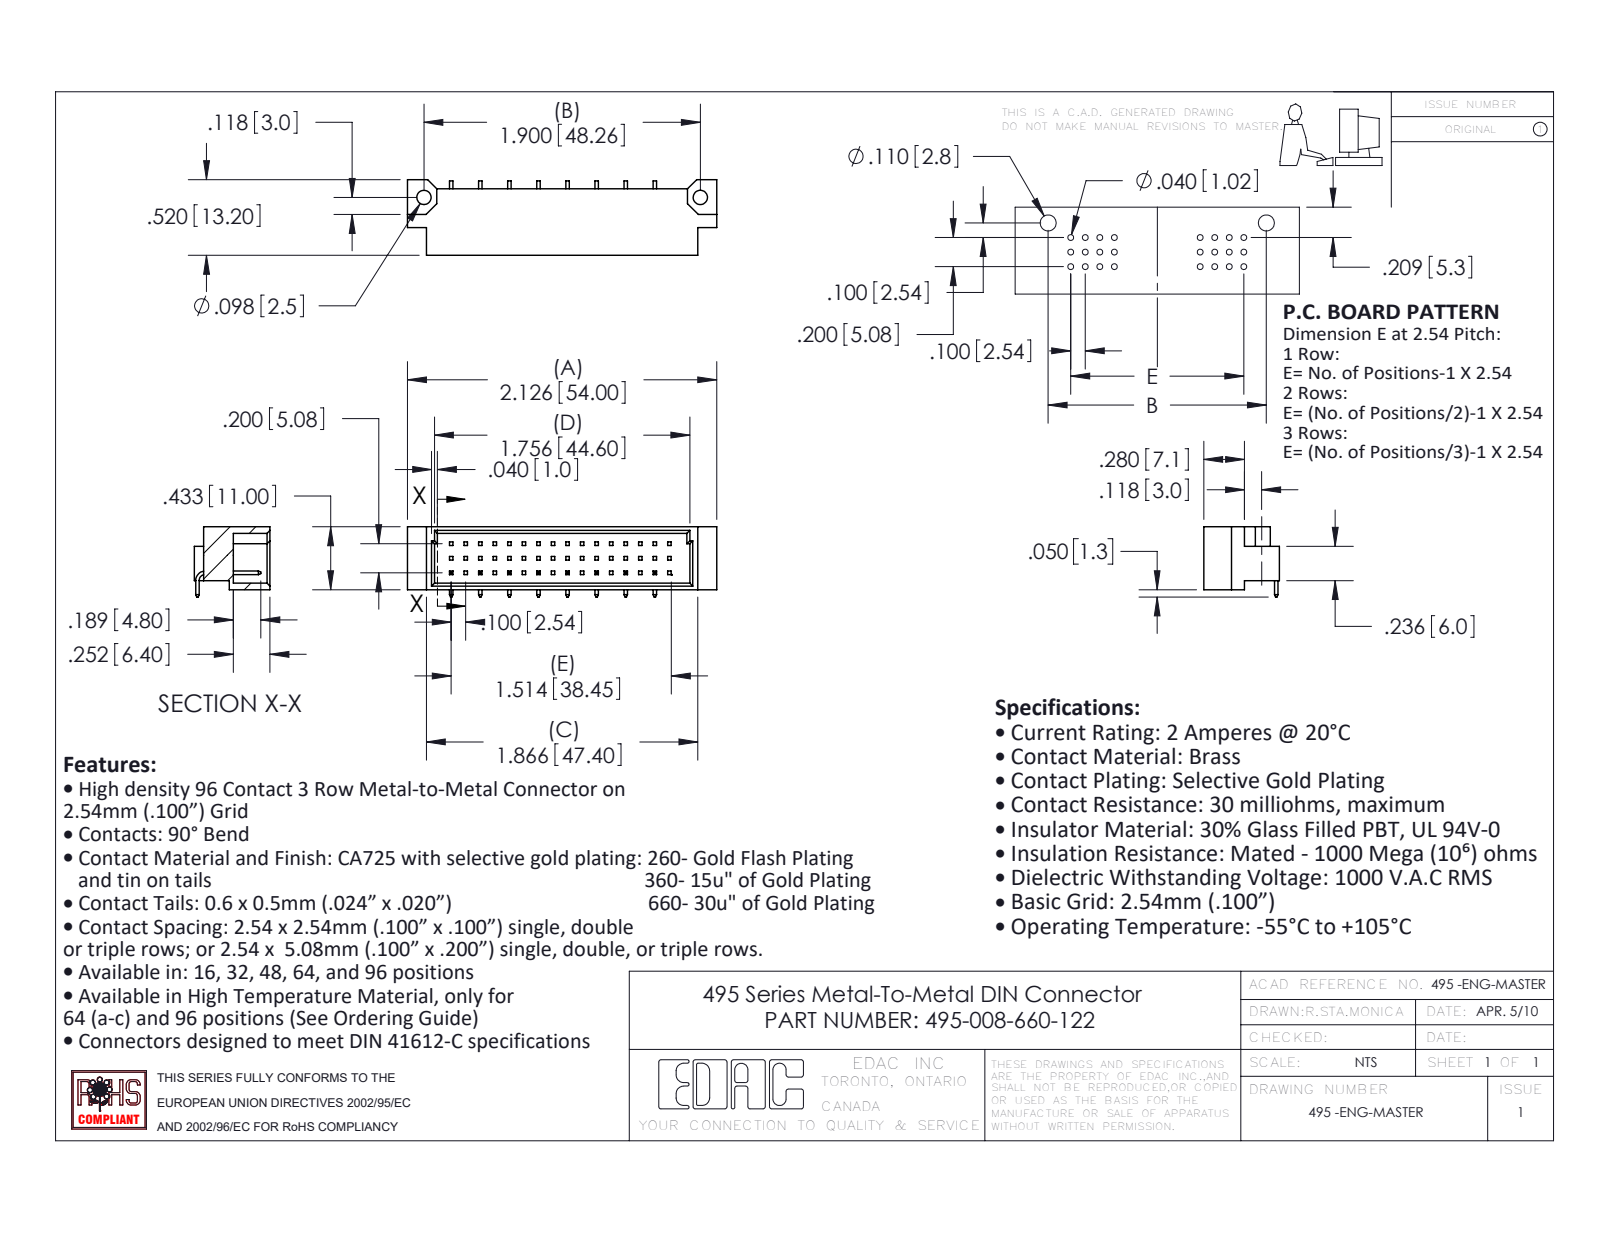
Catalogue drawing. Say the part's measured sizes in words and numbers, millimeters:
The part is named "495-008-260-122; 495 Part_48; 495-290-3". Its 3-D file was written by "SolidWorks 2020 (AUTOMOTIVE_DESIGN)". It is 9 solids with 386 faces: 366 planar, 20 cylindrical and 0 other. Overall it measures 54 by 13.2 by 12.27 millimeters. Its volume is 3 492 cubic millimeters and its surface area 4 247 square millimeters. Round holes: 2 of diameter 2.49. Partial cylindrical surfaces (rounded edges, fillets, slot ends): 1 of radius 1.02, 1 of radius 1.65. The main face-to-face distances are 1.14, 9.86, 5.2, 11, 1.6, 5.08, 8.72, 9.4, 0.46, 8.26. The hole center spacings are 48.26.
